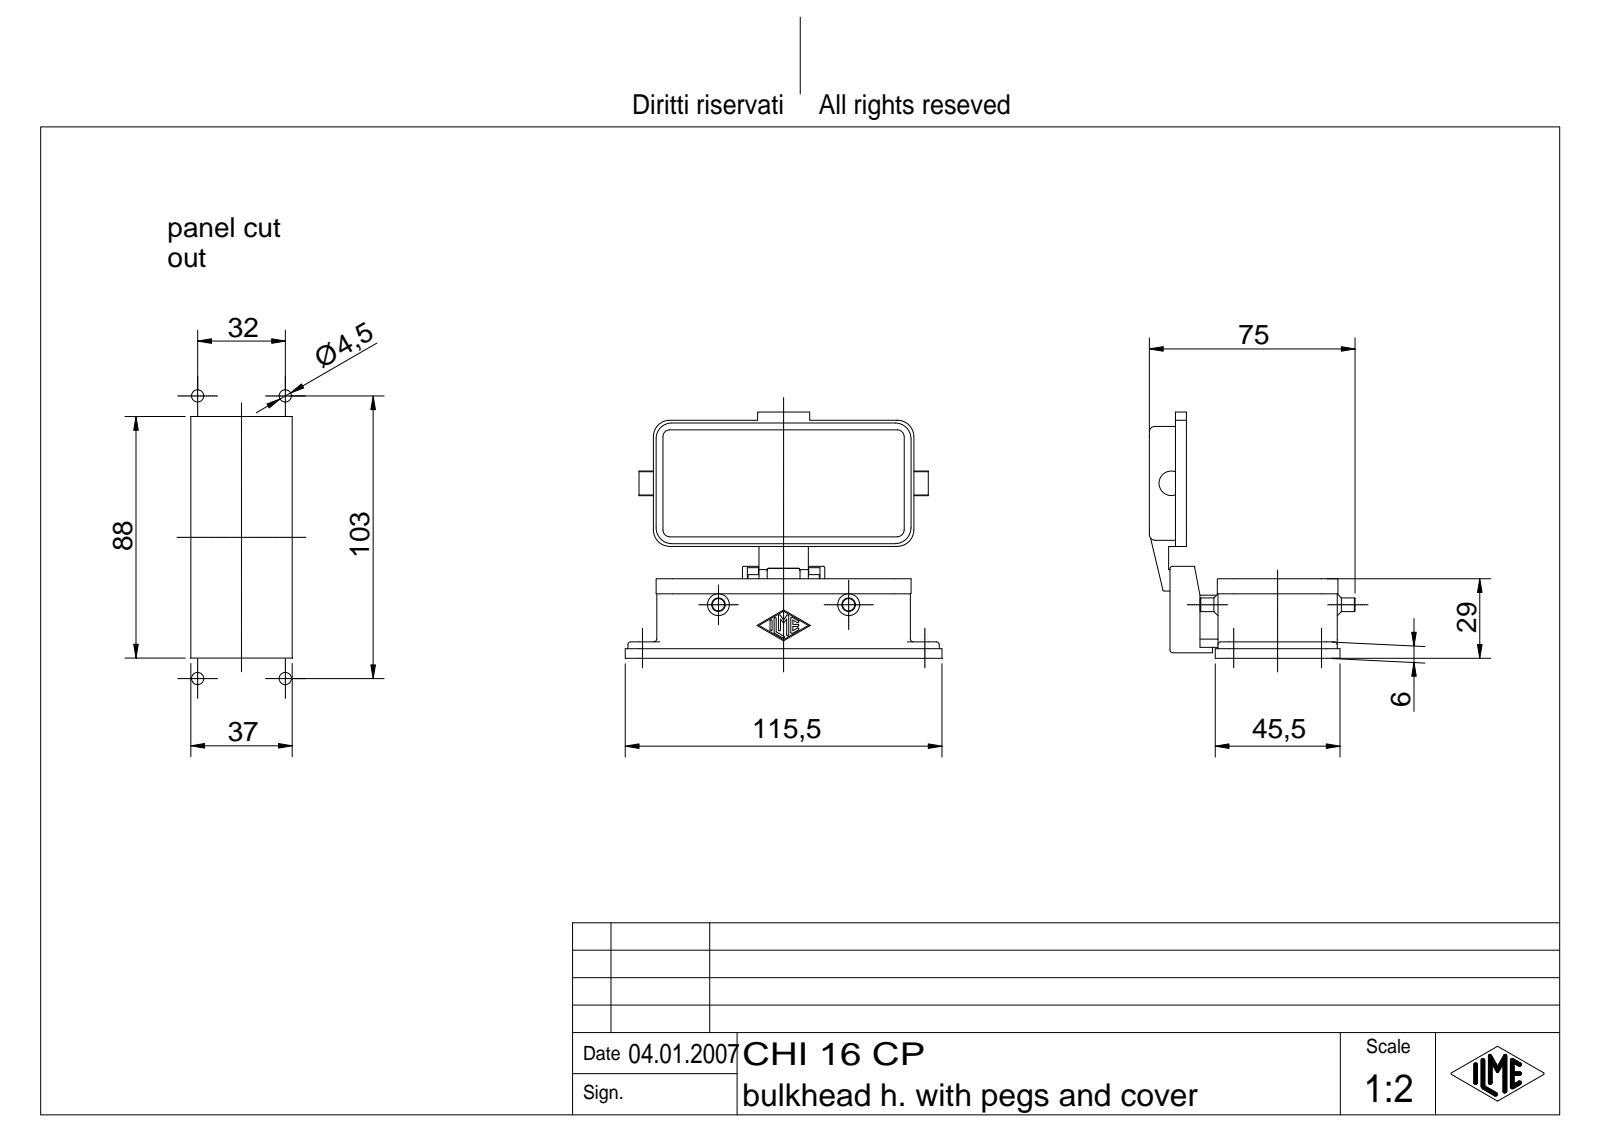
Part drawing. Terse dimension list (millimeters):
name: CHI 16 CP
written by: Autodesk Inventor 7 (AUTOMOTIVE_DESIGN)
unit: mm
bodies: 1 solid, 470 faces (205 planar, 179 cylindrical, 86 other)
size: 115.5 × 89.75 × 75
volume: 56 542 mm³; area: 42 153 mm²
holes: 4× ⌀4.5, 4× ⌀4.6, 1× ⌀4, 1× ⌀5
bosses: 2× ⌀5, 2× ⌀3, 1× ⌀7, 1× ⌀4
rounds: 14× R0.38, 12× R6, 10× R0.5, 8× R0.7, 8× R1, 8× R2, 8× R2.5, 4× R3
face distances: 2.5, 3, 4, 40.5, 0.75, 1.25, 40.75, 1, 2, 25.5
hole spacings: 32, 103, 107.86
